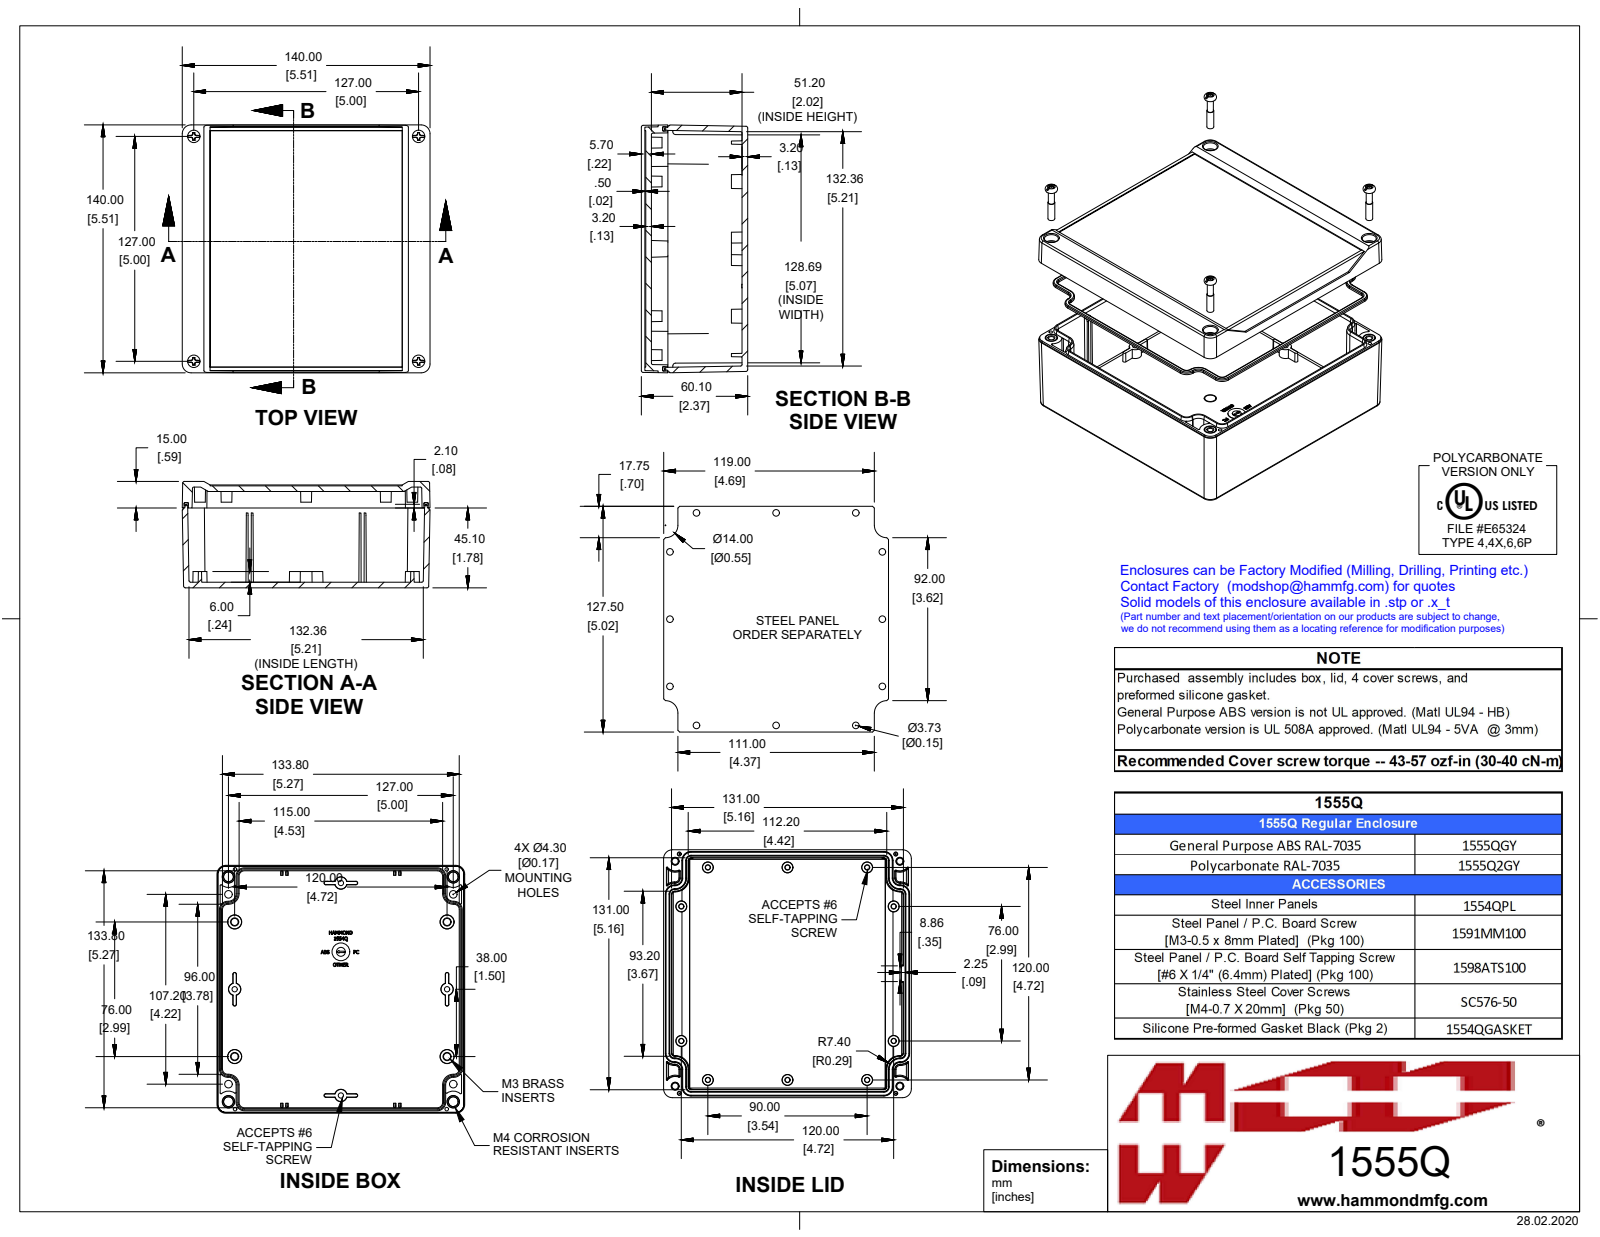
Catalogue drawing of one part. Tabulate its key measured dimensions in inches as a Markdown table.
| quantity | value |
| --- | --- |
| part name | 1555QGY |
| STEP written by | SolidWorks 2019 (AUTOMOTIVE_DESIGN) |
| units | inches |
| bodies | 15 solids, 1945 faces (648 planar, 381 cylindrical, 916 other) |
| overall size | 5.512 × 5.512 × 2.366 |
| volume | 14.5 in³ |
| surface area | 256.5 in² |
| round holes (diameter × count) | 0.097 × 4, 0.128 × 4, 0.181 × 4, 0.138 × 3 |
| round bosses / shafts (diameter × count) | 0.25 × 4, 0.218 × 4, 0.21 × 4, 0.19 × 4, 0.154 × 4, 0.153 × 4, 0.15 × 4, 0.135 × 4 |
| partial cylindrical surfaces (radius × count) | 0.02 × 26, 0.012 × 22, 0.039 × 12, 0.031 × 10, 0.104 × 8, 0.197 × 8, 0.199 × 8, 0.118 × 4 |
| main face-to-face distances | 0.126, 2.142, 0.122, 2.268, 2.016, 5.39, 5.512, 0.098, 5.335, 0.177 |
| hole center spacings | 1.013, 3.998, 4.965, 5, 6.294, 2.992, 4.724, 5.592 |
